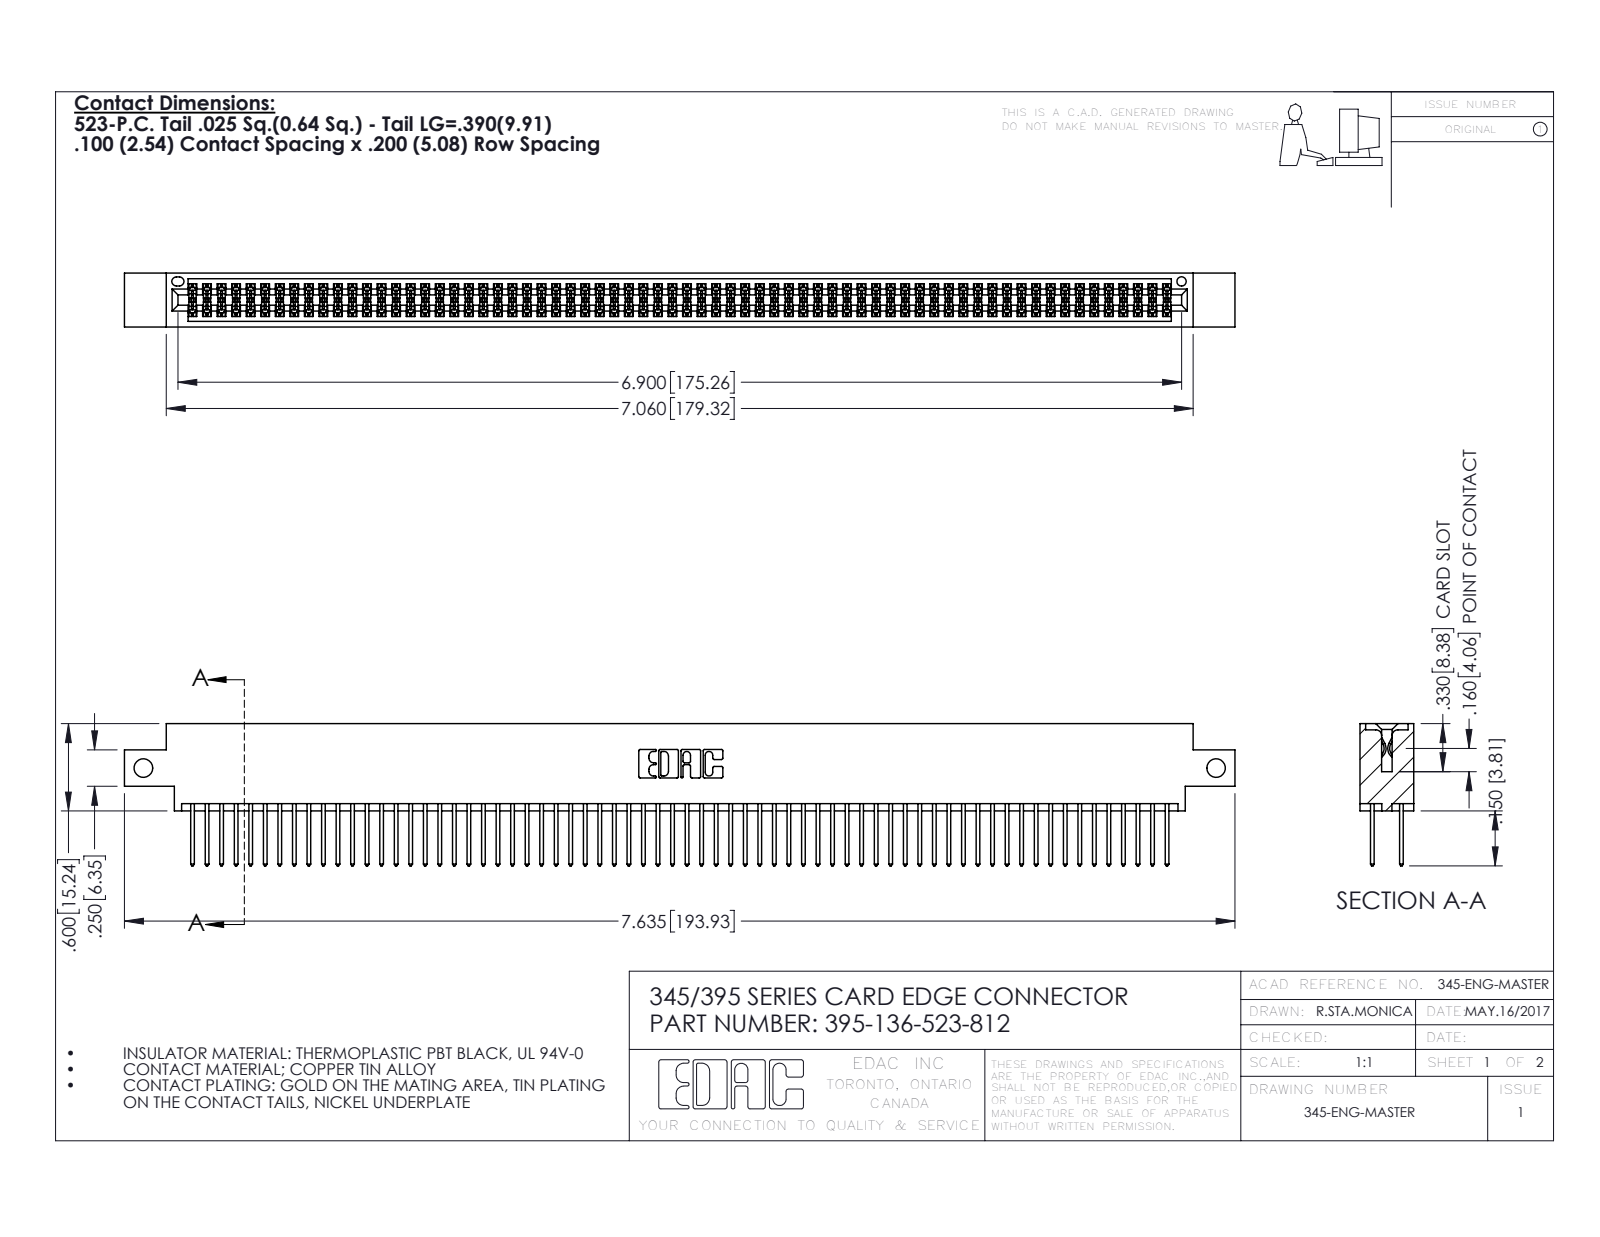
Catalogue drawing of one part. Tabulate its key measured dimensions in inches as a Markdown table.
| quantity | value |
| --- | --- |
| part name | 345 Part_0.170 Offset - Side Mount; 395-136-523-812; 345-292-001_345-293-123 |
| STEP written by | SolidWorks 2016 (CONFIG_CONTROL_DESIGN) |
| units | inches |
| bodies | 137 solids, 6930 faces (4572 planar, 2358 cylindrical, 0 other) |
| overall size | 7.635 × 0.977 × 0.37 |
| volume | 1.169 in³ |
| surface area | 46.62 in² |
| round holes (diameter × count) | 0.128 × 2, 0.064 × 1 |
| partial cylindrical surfaces (radius × count) | 0.006 × 204, 0.01 × 136, 0.01 × 22, 0.007 × 6, 0.031 × 6, 0.026 × 3, 0.014 × 2, 0.019 × 2 |
| main face-to-face distances | 0.072, 0.298, 0.2, 0.098, 0.272, 0.025, 0.37, 0.225, 0.175, 0.149 |
| hole center spacings | 7.375 |
